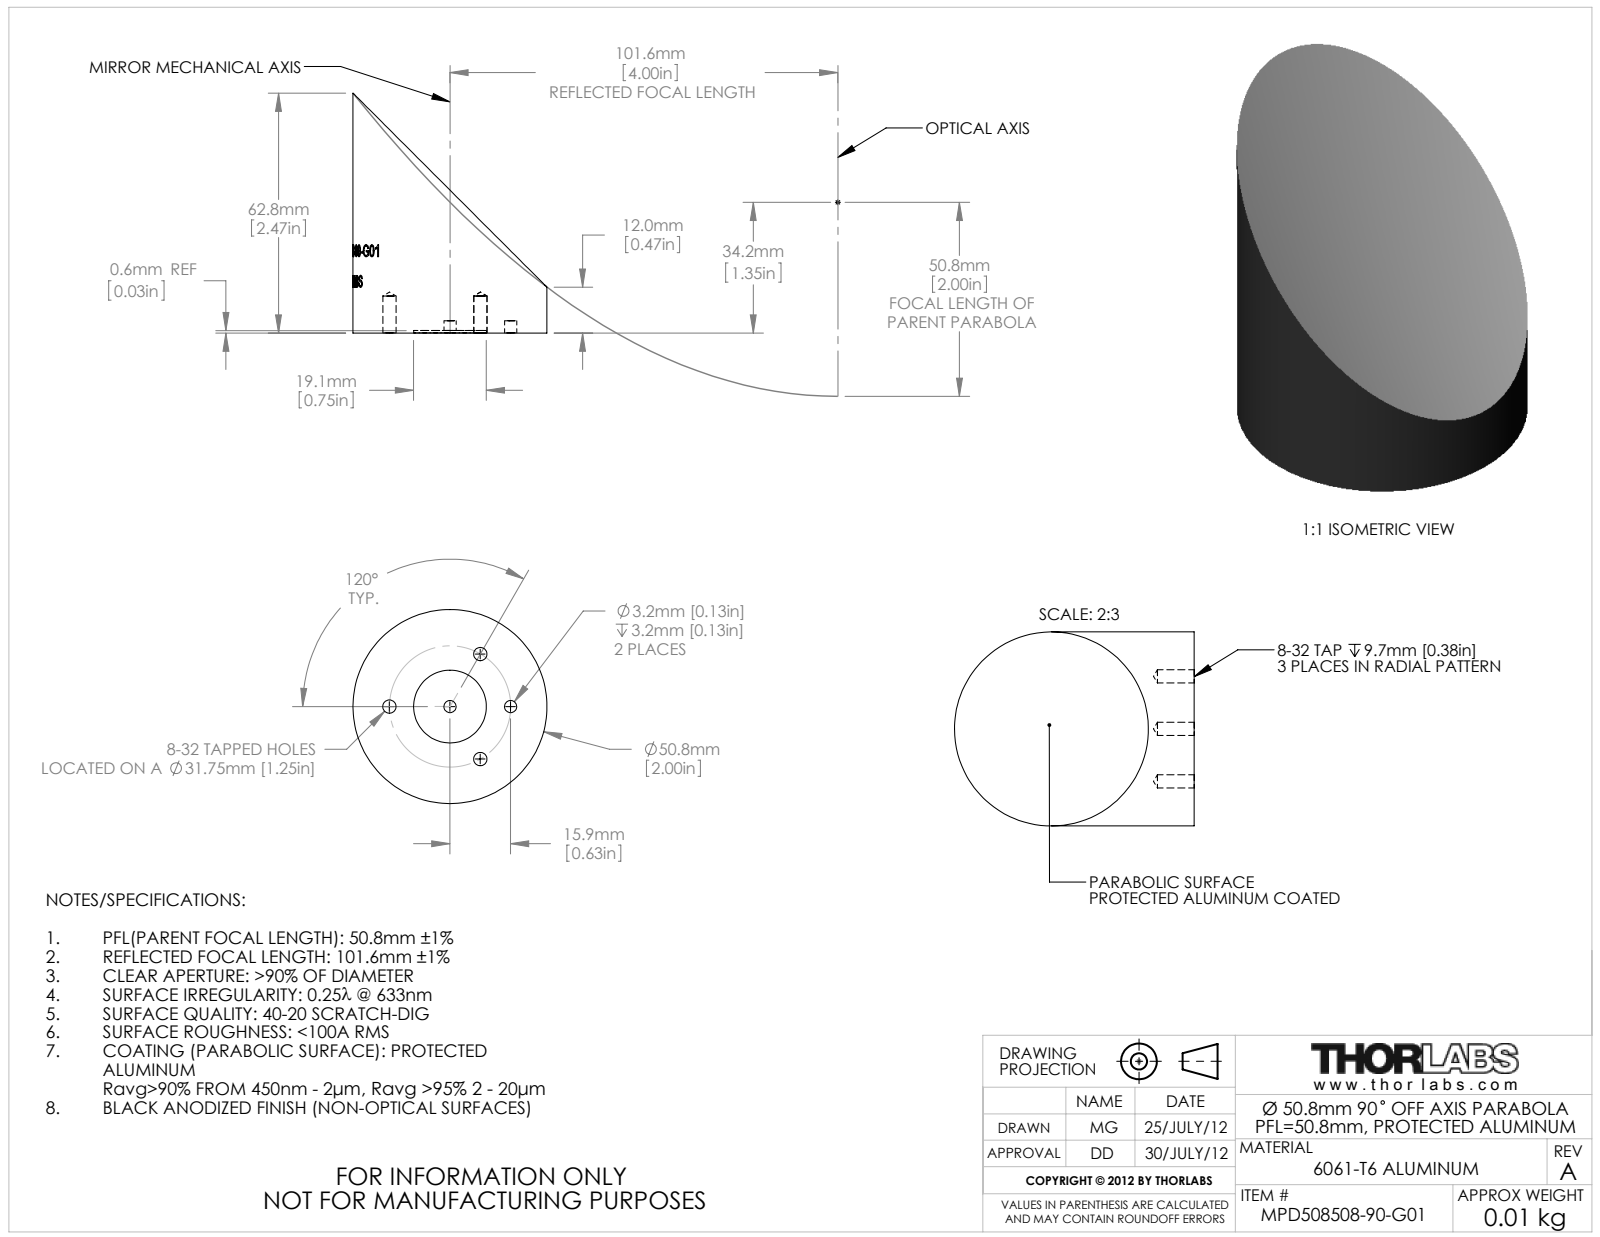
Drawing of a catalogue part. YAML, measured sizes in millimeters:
part_name: "24698-E0W"
step_written_by: "SolidWorks 2012 (CONFIG_CONTROL_DESIGN)"
units: millimeters
bodies: {solids: 1, faces: 66, planar: 4, cylindrical: 54, other: 8}
overall_size: [62.8, 50.8, 50.8]
volume: 72082
surface_area: 11294
round_holes:
  - {diameter: 3.45, count: 3}
  - {diameter: 3.19, count: 2}
  - {diameter: 19.05, count: 1}
round_bosses_or_shafts:
  - {diameter: 50.8, count: 1}
face_to_face_distances: [0.64, 3.17, 2.53]
hole_center_spacings: [15.88, 27.5, 31.76]
